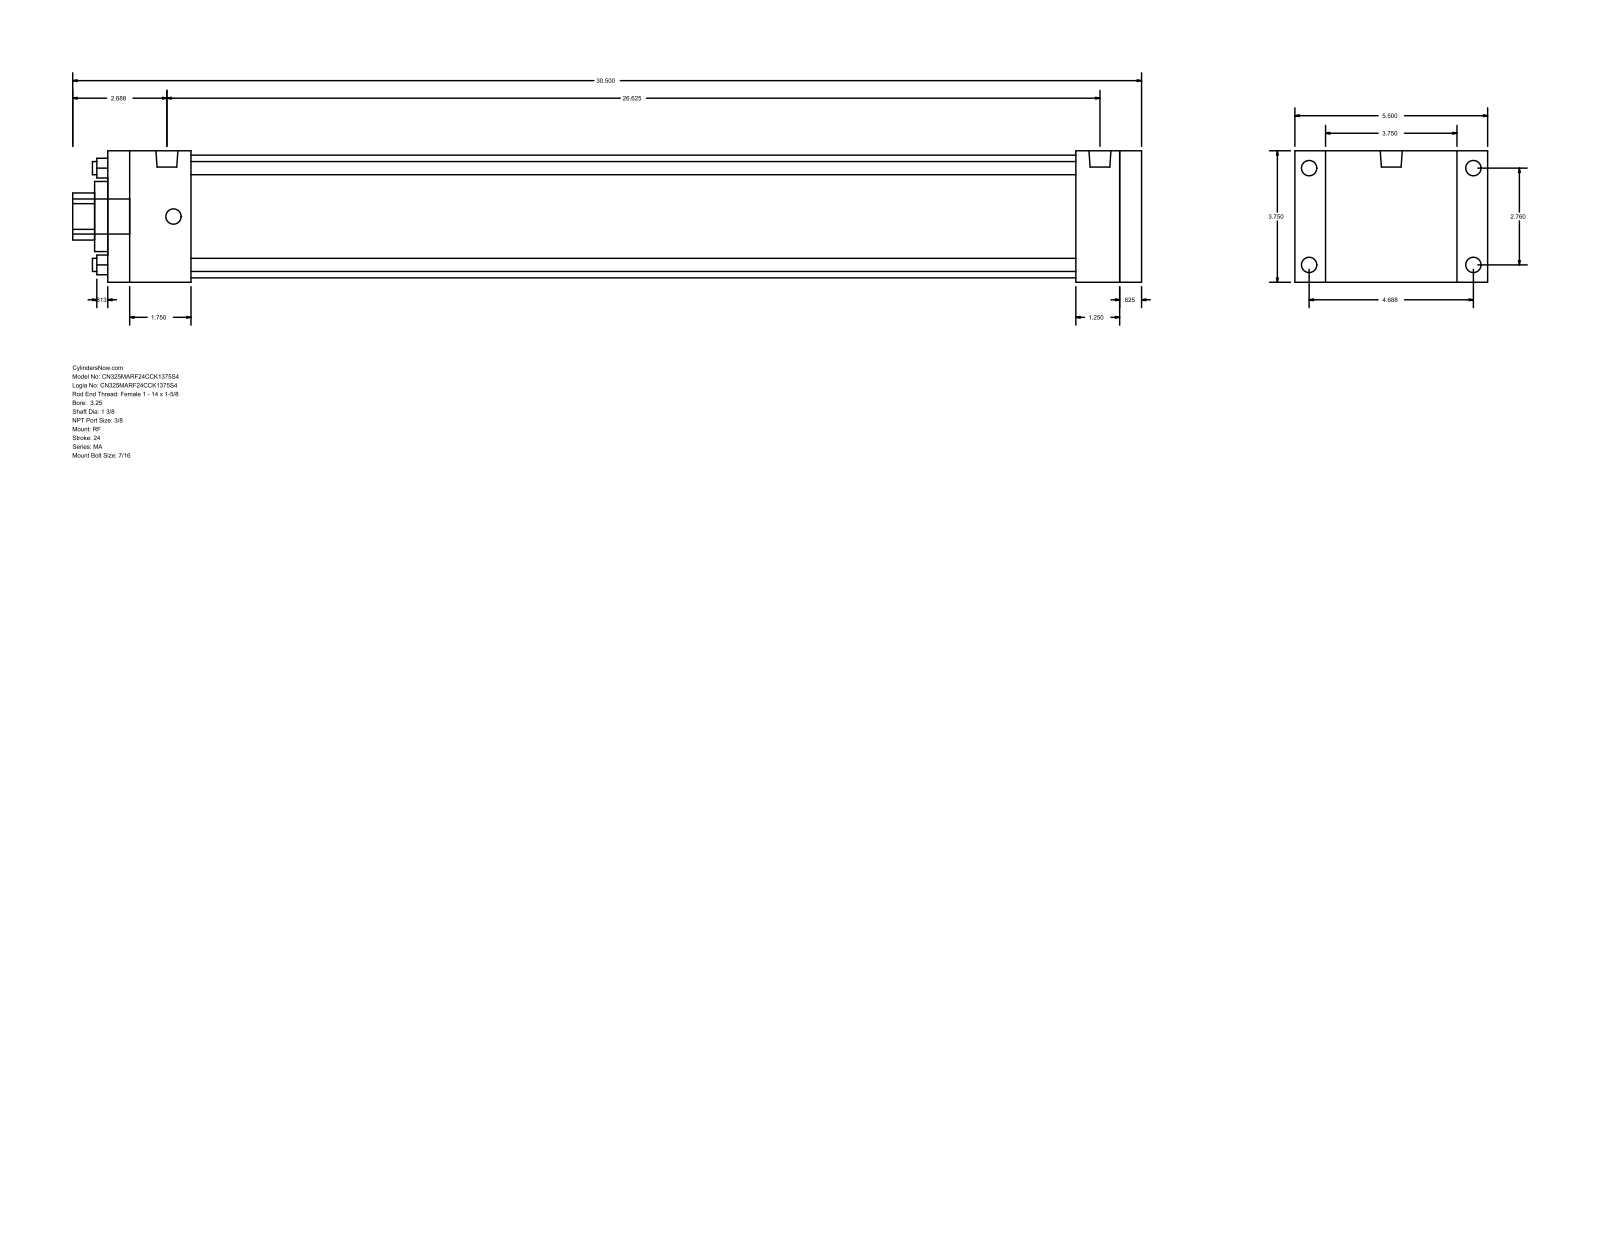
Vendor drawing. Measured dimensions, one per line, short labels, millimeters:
name: MA_RF__0325_1.375
written by: GSSL Pune (CONFIG_CONTROL_DESIGN)
unit: mm
bodies: 0 solids, 92 faces (64 planar, 28 cylindrical, 0 other)
size: 774.7 × 139.7 × 95.25
holes: 4× ⌀9.53, 1× ⌀34.92, 1× ⌀50.8, 1× ⌀88.9
bosses: 8× ⌀11.11, 2× ⌀15.93, 1× ⌀25.4
rounds: 1× R17.06
face distances: 95.24, 749.3, 15.87, 733.43, 22.23, 117.47, 701.68, 31.75, 47.62, 60.32
hole spacings: 49.57, 70.1, 99.14
